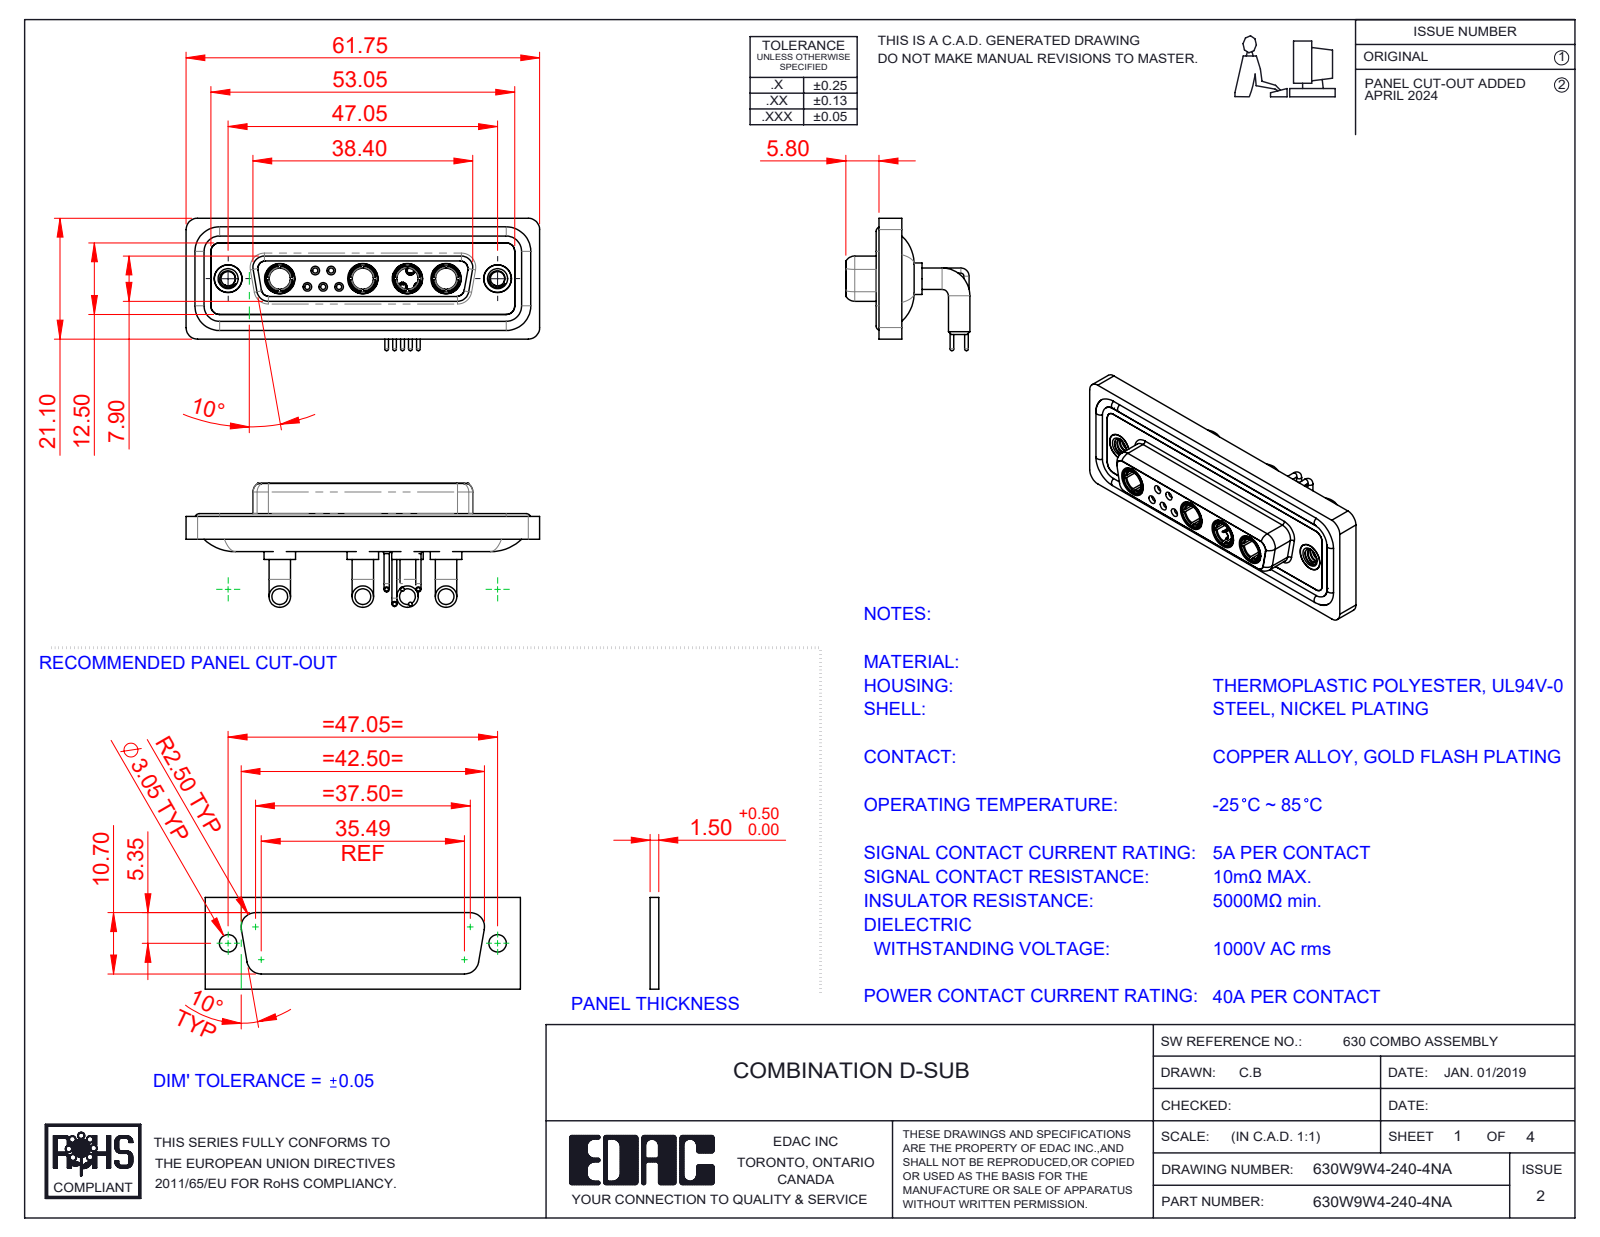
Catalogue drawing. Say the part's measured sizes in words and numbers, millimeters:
The part is named "630W9W4-140-4NA; Power Socket_40A RA; 630Combo Contact Row 1_50 Contacts; 630Combo Housing_9W4 (+5 more)". Its 3-D file was written by "SolidWorks 2023 (CONFIG_CONTROL_DESIGN)". It is 20 solids with 957 faces: 296 planar, 401 cylindrical and 260 other. Overall it measures 61.75 by 23.12 by 21.68 millimeters. Its volume is 8 735 cubic millimeters and its surface area 14 225 square millimeters. Round holes: 6 of diameter 4.85, 5 of diameter 0.9, 5 of diameter 1.1, 5 of diameter 1.5, 5 of diameter 2, 4 of diameter 3.7, 4 of diameter 5.3, 3 of diameter 1.6, 2 of diameter 1.7, 2 of diameter 2.5, 2 of diameter 4, 2 of diameter 4.05. Round bosses or shafts: 10 of diameter 0.9, 9 of diameter 1.6, 8 of diameter 3.75, 5 of diameter 2, 5 of diameter 1.5, 5 of diameter 0.65, 4 of diameter 5.5, 4 of diameter 5.2. Partial cylindrical surfaces (rounded edges, fillets, slot ends): 18 of radius 1.5, 18 of radius 2, 8 of radius 1.35, 8 of radius 1.6, 4 of radius 0.25, 4 of radius 0.5, 4 of radius 0.6, 4 of radius 0.65. The main face-to-face distances are 0.4, 1.8, 4.1, 1.1, 1.6, 2.5, 3.1, 3.7, 1.5, 1.4. The hole center spacings are 3.16, 2.77, 5.04, 13.85, 11.08, 12.79, 15.5, 5.54.
